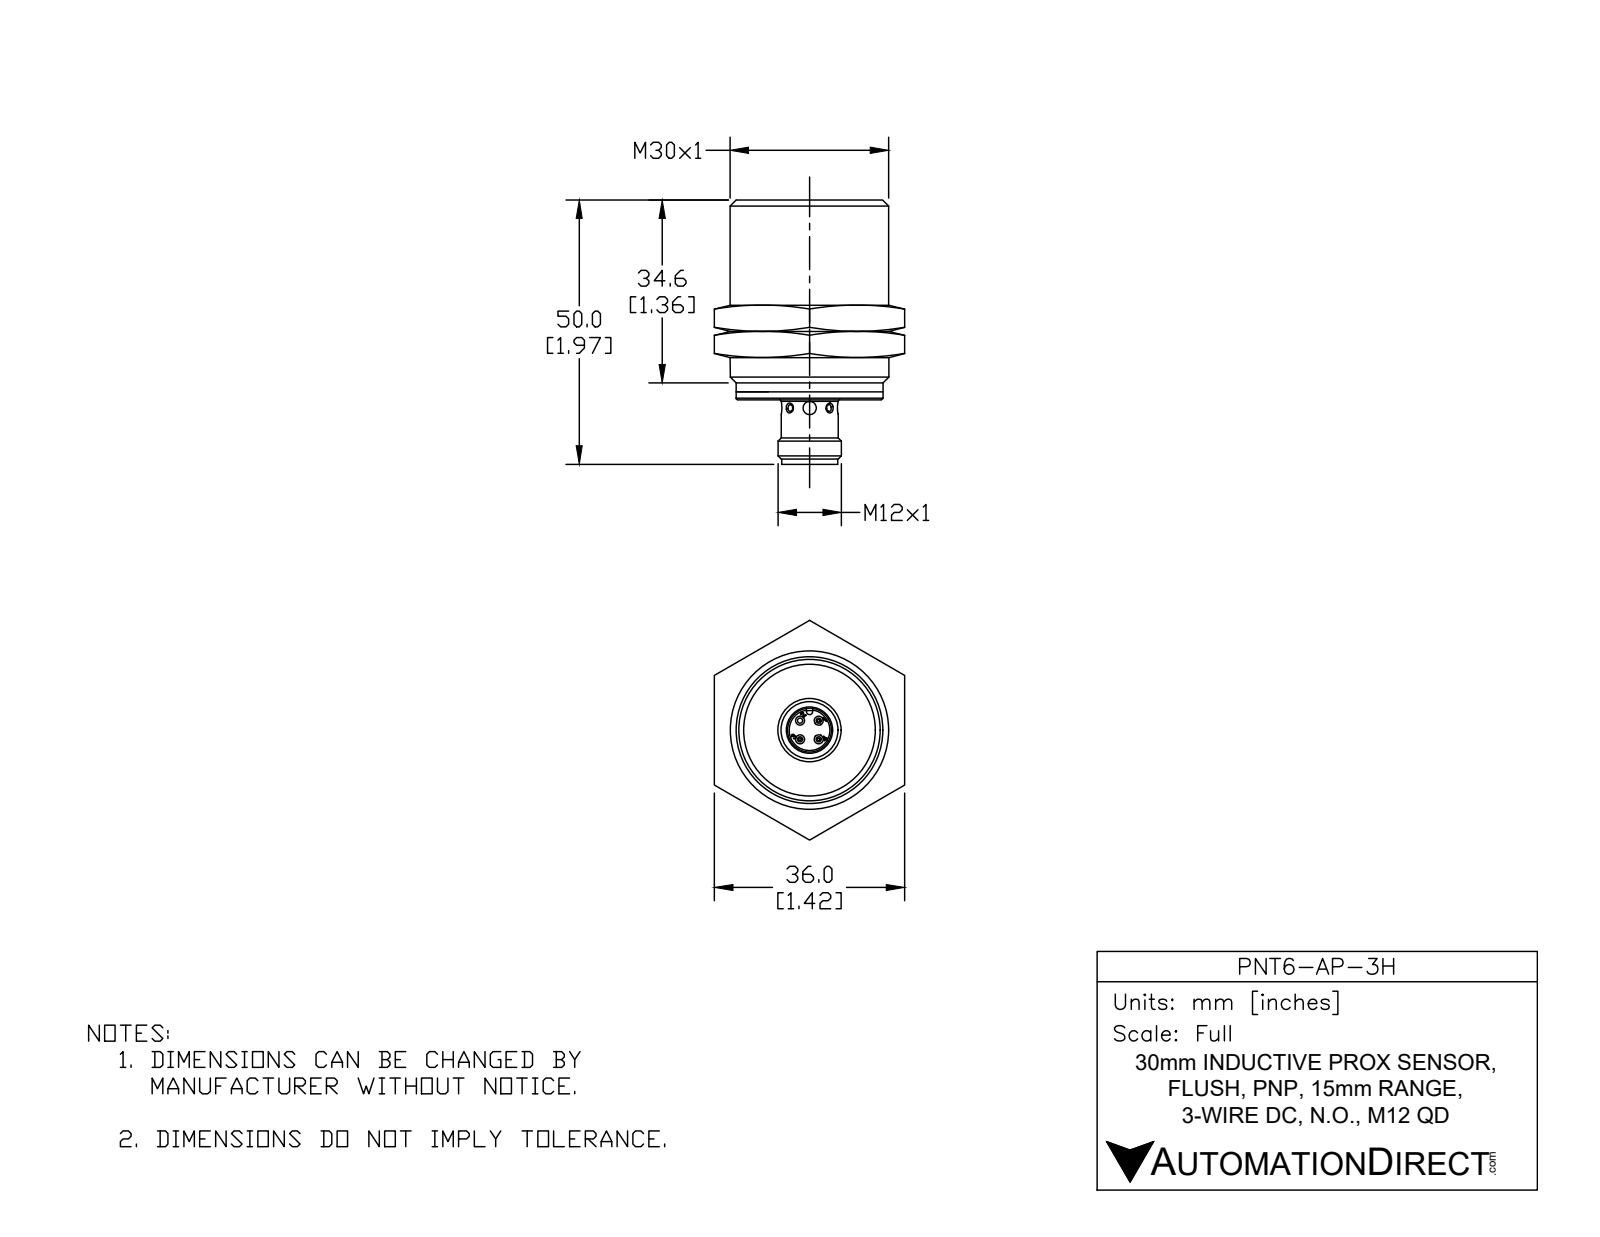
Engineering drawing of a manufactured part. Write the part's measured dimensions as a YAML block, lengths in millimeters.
part_name: "PNT6-AP-3H"
step_written_by: "SolidWorks 2017 (AUTOMOTIVE_DESIGN)"
units: millimeters
bodies: {solids: 1, faces: 515, planar: 161, cylindrical: 130, other: 224}
overall_size: [50, 30, 30]
volume: 25780
surface_area: 8252
round_holes:
  - {diameter: 1.1, count: 3}
  - {diameter: 1, count: 2}
  - {diameter: 2.5, count: 2}
  - {diameter: 1, count: 1}
  - {diameter: 1, count: 1}
  - {diameter: 8.2, count: 1}
  - {diameter: 8.3, count: 1}
  - {diameter: 10, count: 1}
  - {diameter: 26.6, count: 1}
  - {diameter: 27.3, count: 1}
  - {diameter: 27.7, count: 1}
round_bosses_or_shafts:
  - {diameter: 1, count: 9}
  - {diameter: 30, count: 1}
  - {diameter: 27.8, count: 1}
  - {diameter: 27.5, count: 1}
  - {diameter: 27.3, count: 1}
  - {diameter: 26.5, count: 1}
  - {diameter: 22.3, count: 1}
  - {diameter: 12, count: 1}
partial_cylinders:
  - {radius: 0.1, count: 12}
  - {radius: 0.5, count: 8}
  - {radius: 0.8, count: 3}
  - {radius: 1, count: 3}
  - {radius: 0.6, count: 1}
  - {radius: 0.8, count: 1}
face_to_face_distances: [3.2, 37.8, 34.6, 0.9, 2.3, 36.9, 2.5, 37.1, 0.7, 0.6]
hole_center_spacings: [2.5, 3.5, 5]
